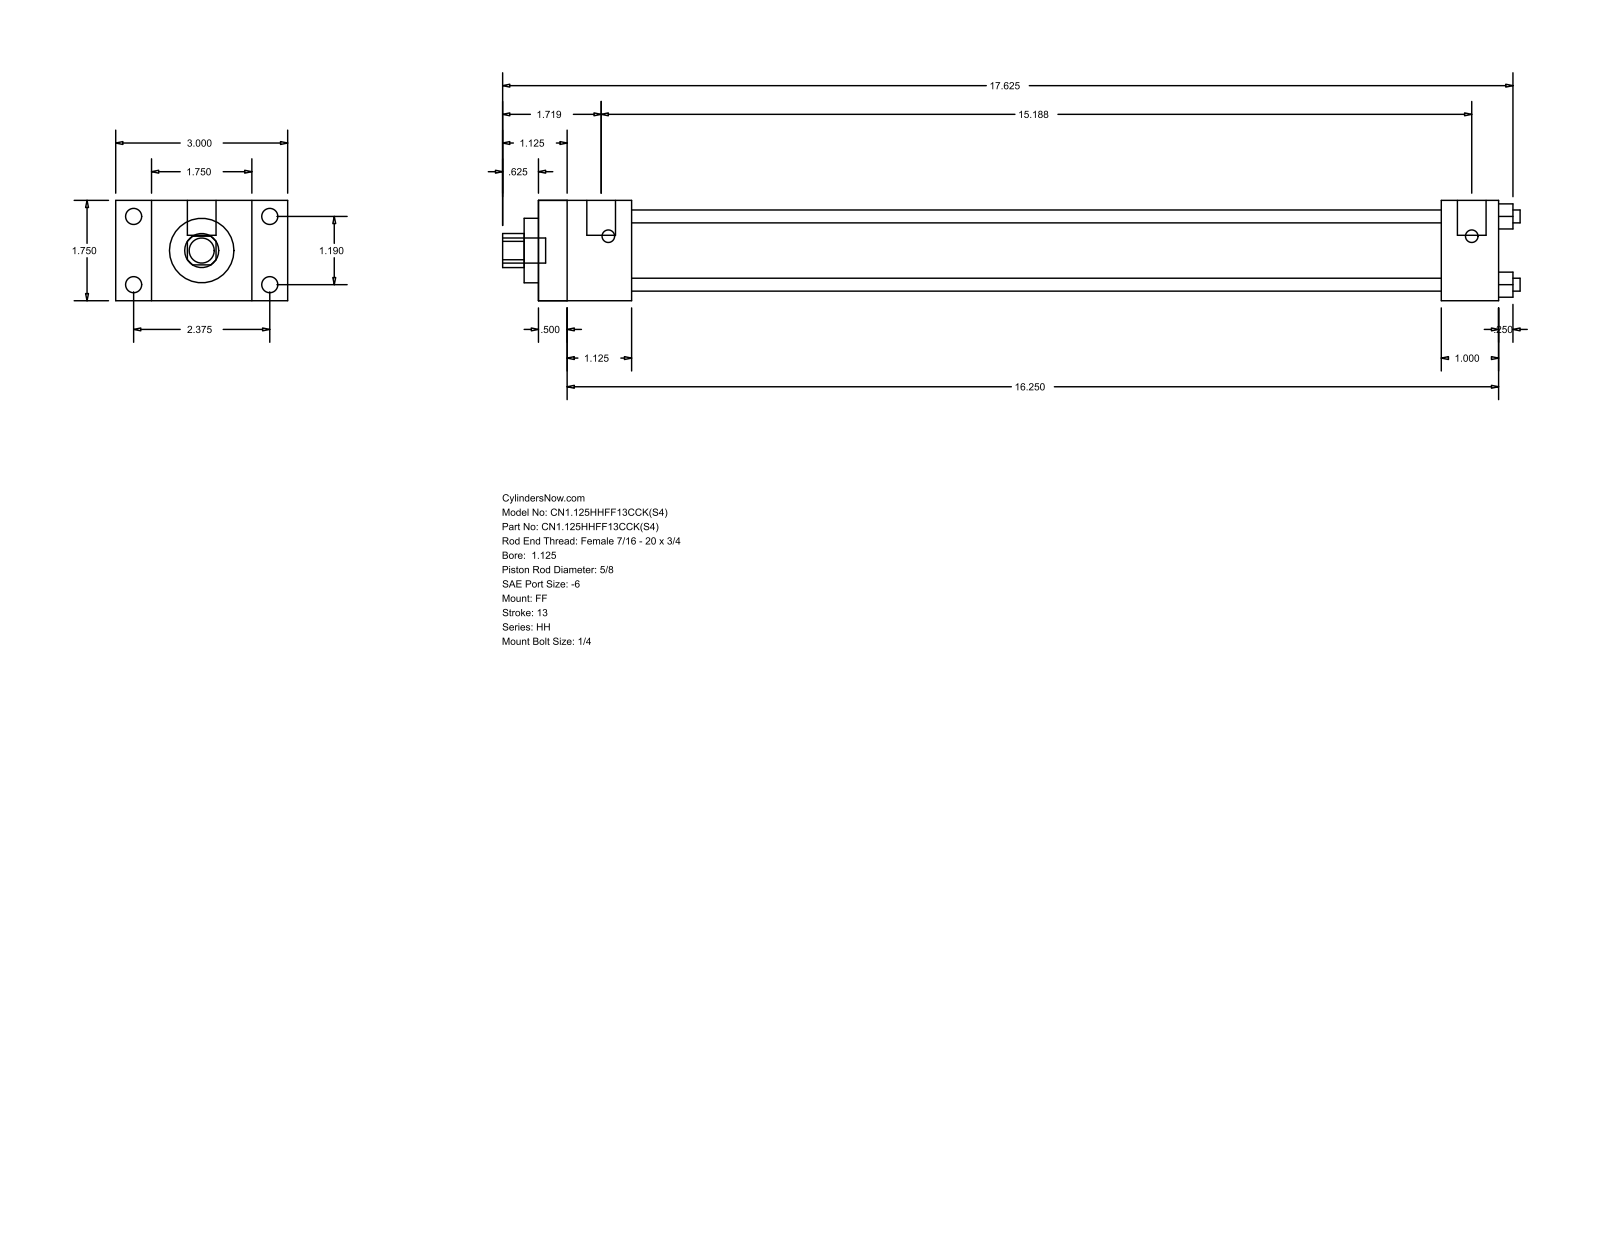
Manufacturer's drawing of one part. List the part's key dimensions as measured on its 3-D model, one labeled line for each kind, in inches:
Part name (STEP PRODUCT): HH_FF__0112_0.625
STEP written by: GSSL Pune (CONFIG_CONTROL_DESIGN)
Units: inches
Bodies: 0 solids, 92 faces (64 planar, 28 cylindrical, 0 other)
Overall size (bounding box): 17.75 × 3 × 1.75
Round holes (diameter × count): ⌀0.225 ×4, ⌀0.625 ×1, ⌀1.125 ×1, ⌀1.375 ×1
Round bosses / shafts (diameter × count): ⌀0.281 ×4, ⌀0.219 ×4, ⌀0.5 ×2, ⌀0.437 ×1
Partial cylindrical surfaces — rounded edges, fillets, slot ends (radius × count): R0.297 ×1
Main face-to-face distances: 1.75, 16.75, 0.5, 16.25, 0.625, 2.375, 1.125, 1.625, 15.75, 15.25
Hole centre spacings: 0.841, 1.19, 1.683
